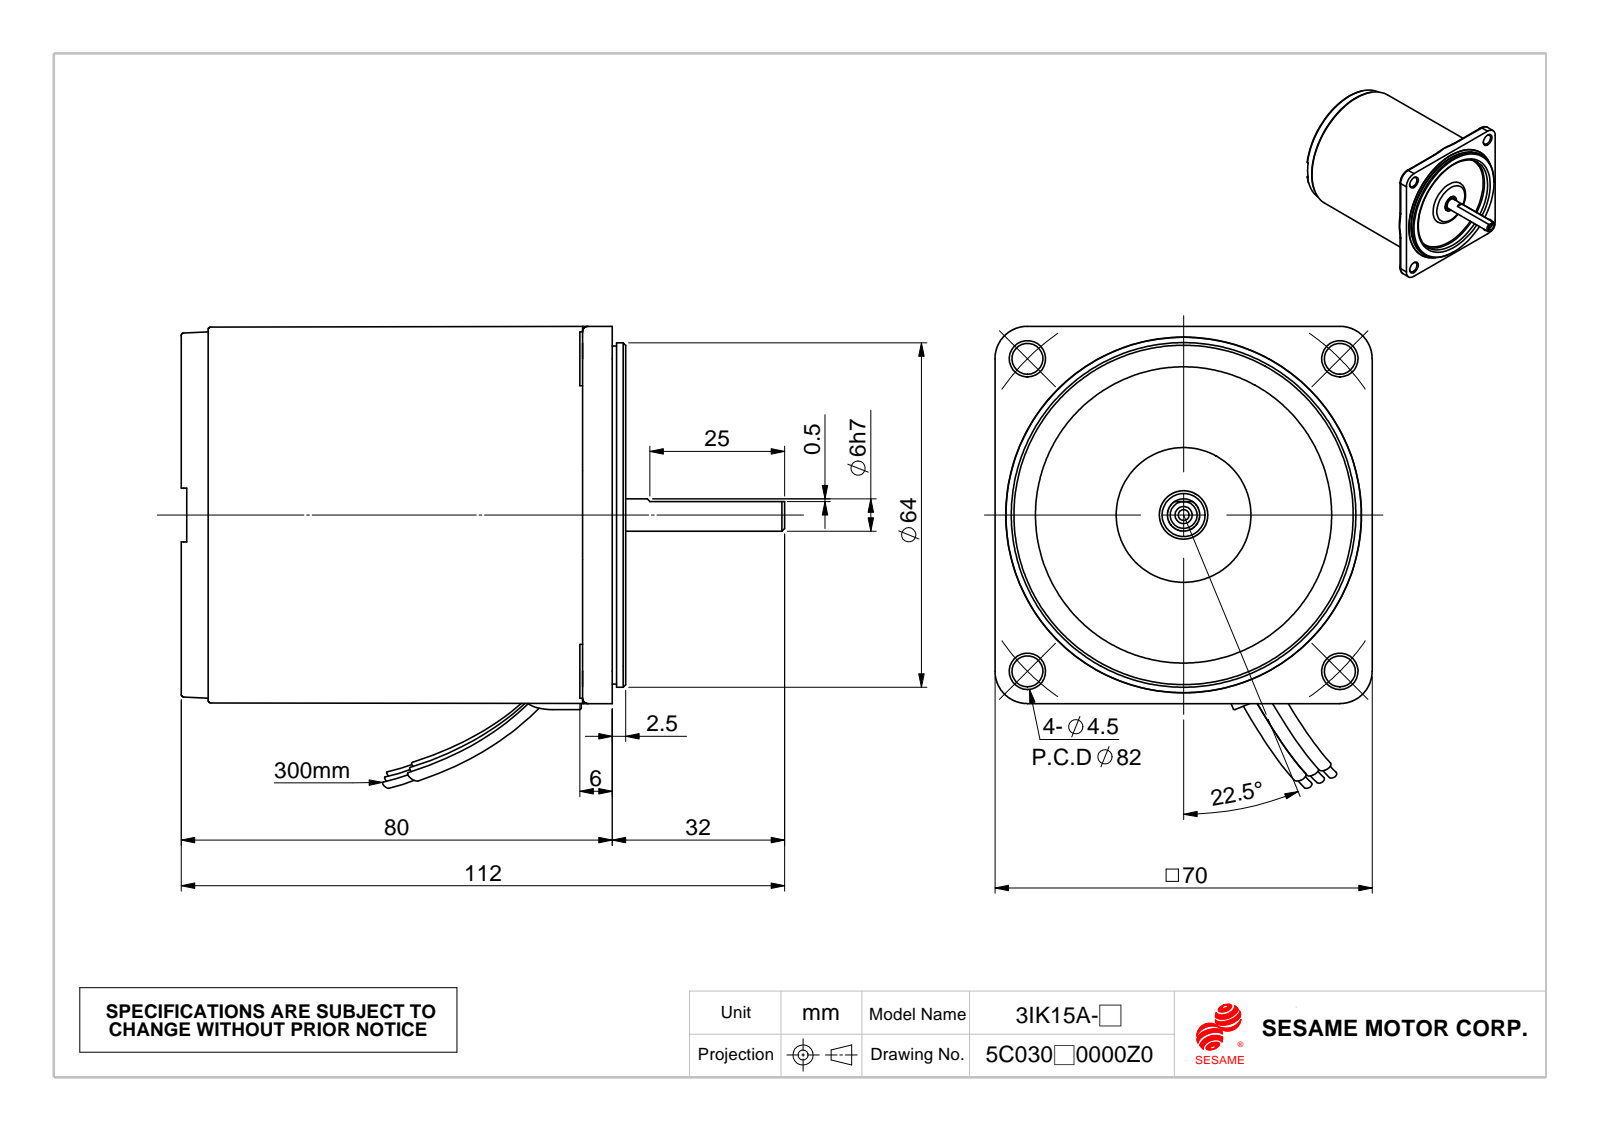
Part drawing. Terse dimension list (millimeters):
name: C364_車工(成品); M315_2車工; 15A_0.成品; 線扣
written by: SolidWorks 2010 (CONFIG_CONTROL_DESIGN)
unit: mm
bodies: 7 solids, 244 faces (75 planar, 78 cylindrical, 91 other)
size: 112 × 85.74 × 70
volume: 312 248 mm³; area: 39 402 mm²
holes: 4× ⌀5.75, 1× ⌀2, 1× ⌀7.2, 1× ⌀9, 1× ⌀9.5, 1× ⌀18, 1× ⌀55, 1× ⌀58.2, 1× ⌀60.5, 1× ⌀66
bosses: 4× ⌀10, 1× ⌀63.93, 1× ⌀62.73, 1× ⌀57.42, 1× ⌀57.2, 1× ⌀9.3, 1× ⌀8, 1× ⌀7.4
rounds: 8× R0.25, 4× R1, 4× R6, 1× R5.25, 1× R33.98
face distances: 77.4, 77.5, 1.51, 75.89, 1.61, 1.5, 79, 3.11, 1.6, 4
hole spacings: 41.01, 58, 82.02
